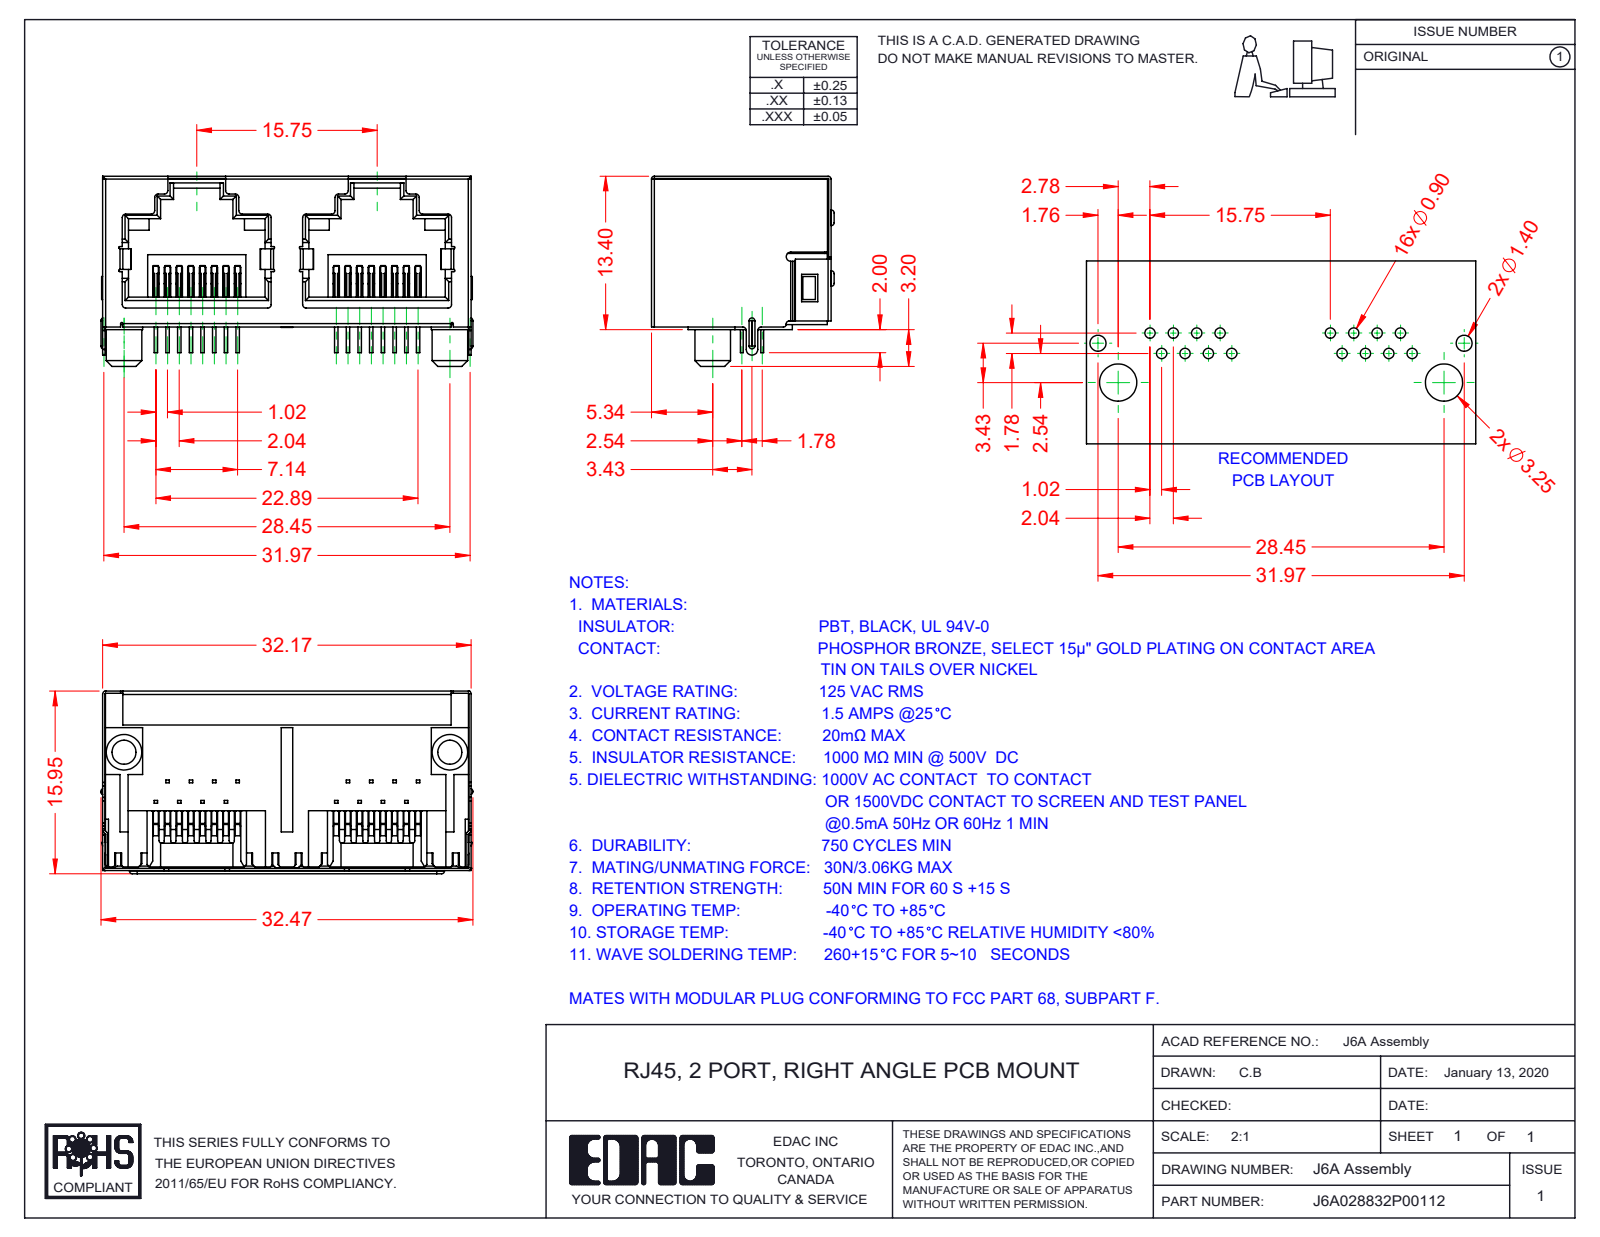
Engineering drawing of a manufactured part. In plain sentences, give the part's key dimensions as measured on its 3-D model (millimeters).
The part is named "6A Shield; 6A Contacts; 6A Insulator; J6A028832P00112". Its 3-D file was written by "SolidWorks 2016 (CONFIG_CONTROL_DESIGN)". It is 18 solids with 1823 faces: 1380 planar, 415 cylindrical and 28 other. Overall it measures 32.47 by 16.6 by 15.95 millimeters. Its volume is 2 964 cubic millimeters and its surface area 8 172 square millimeters. Round bosses or shafts: 2 of diameter 3.1. Partial cylindrical surfaces (rounded edges, fillets, slot ends): 44 of radius 0.1, 44 of radius 0.3, 23 of radius 0.25, 16 of radius 0.2, 14 of radius 0.23, 4 of radius 0.21, 4 of radius 0.47, 4 of radius 0.68. The main face-to-face distances are 15.75, 0.85, 31.97, 12.95, 12.7, 12.75, 15.47, 10.55, 2, 2.4.
